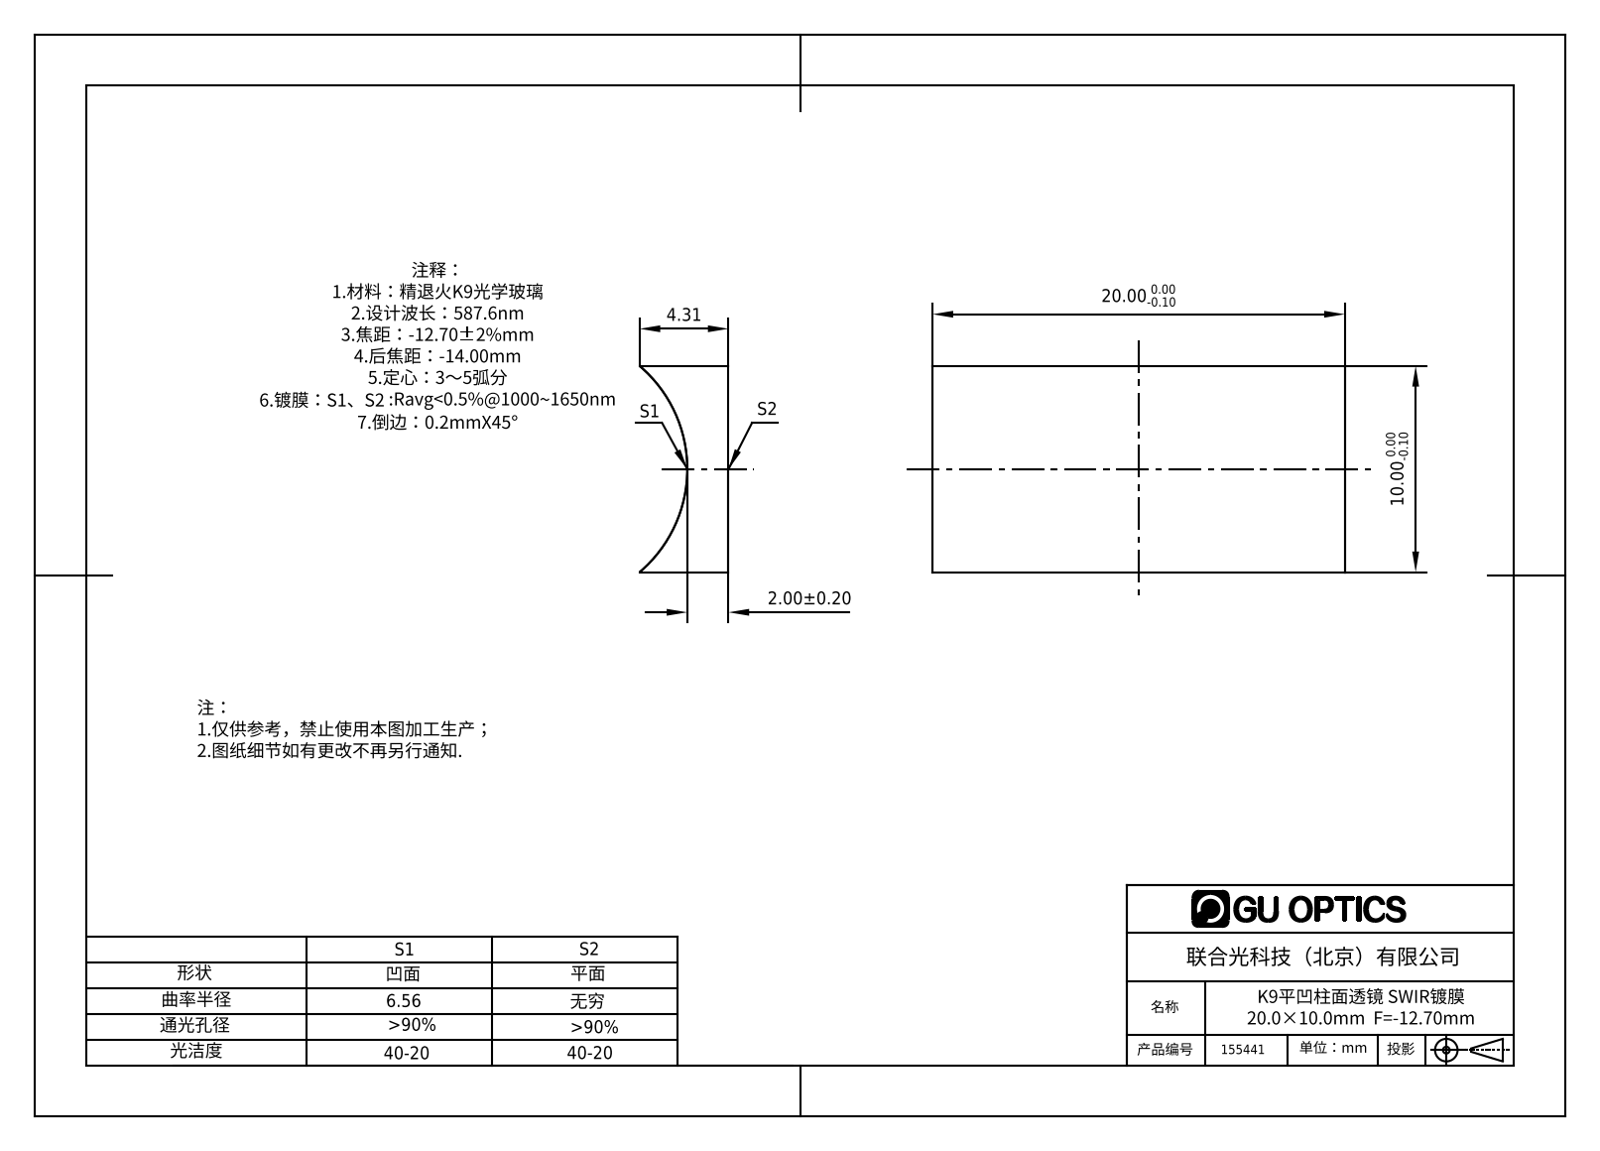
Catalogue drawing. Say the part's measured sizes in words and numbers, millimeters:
The part is named "155342". Its 3-D file was written by "SolidWorks 2016 (AUTOMOTIVE_DESIGN)". It is 1 solid with 6 faces: 5 planar, 1 cylindrical and 0 other. Overall it measures 20 by 10 by 4.31 millimeters. Its volume is 541 cubic millimeters and its surface area 654 square millimeters. Partial cylindrical surfaces (rounded edges, fillets, slot ends): 1 of radius 6.56. The main face-to-face distances are 10, 20.
